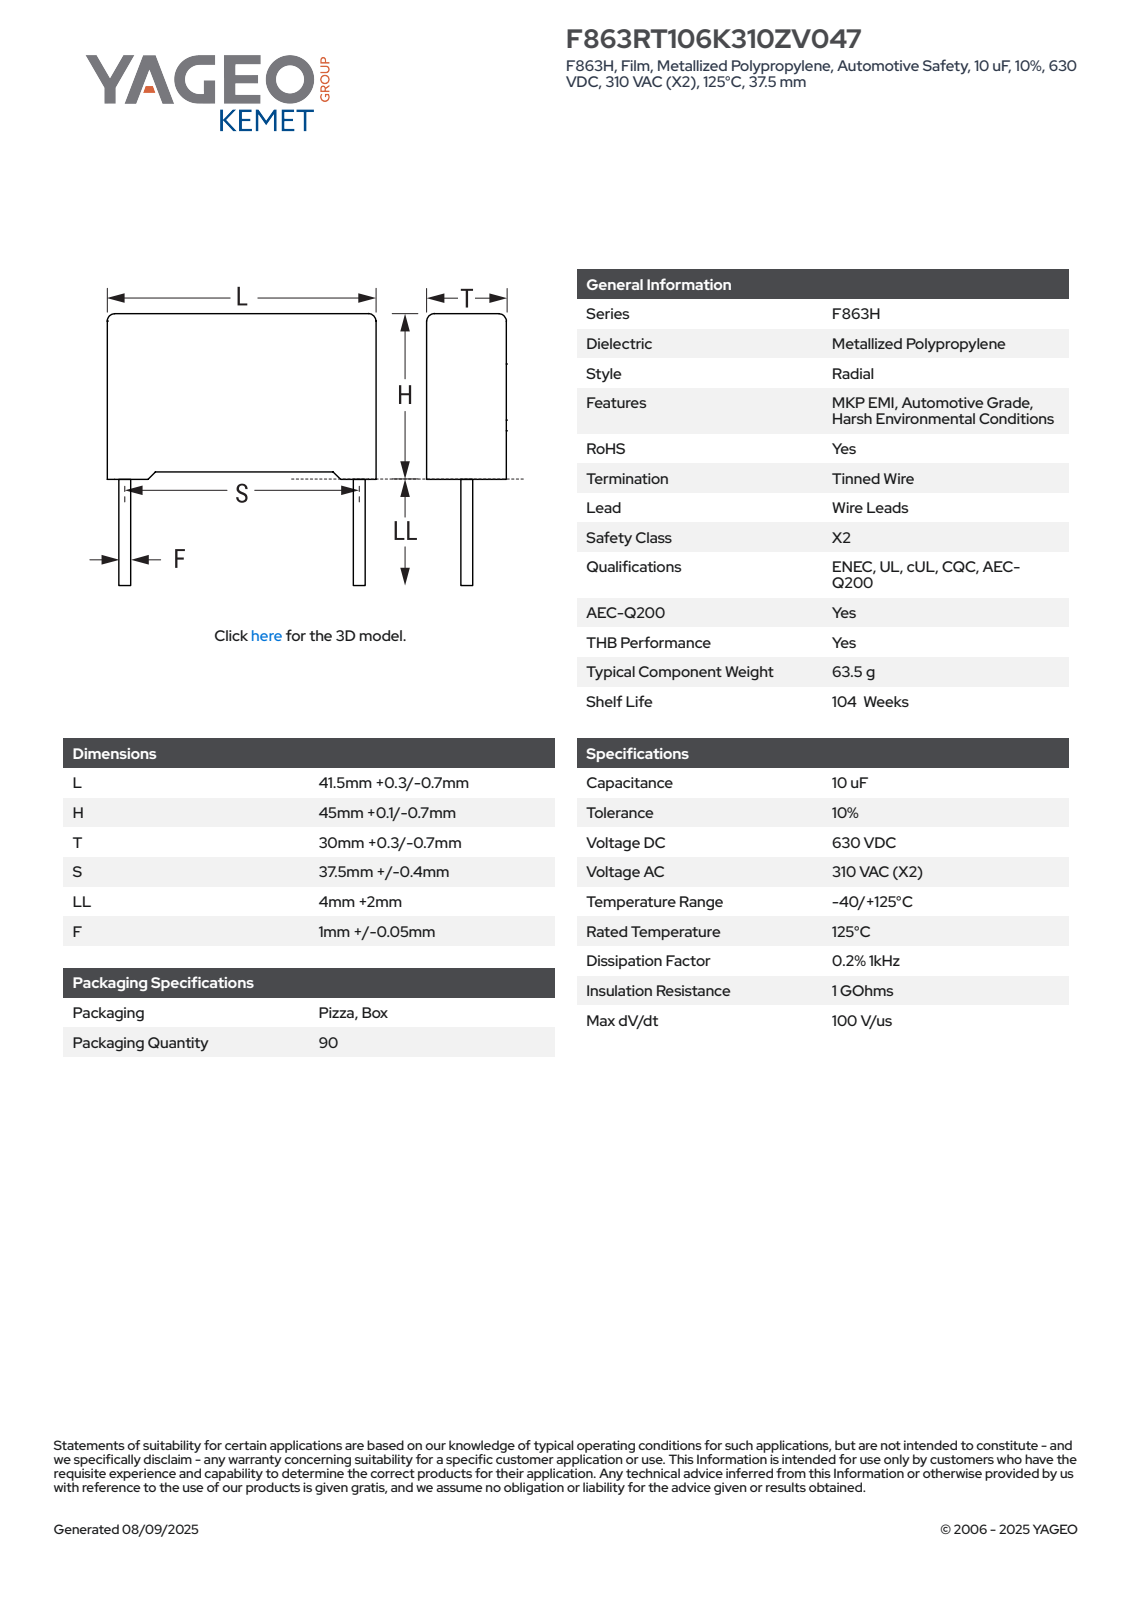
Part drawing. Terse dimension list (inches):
name: CFR_RB2_41.5X45X30_L41.8H45.1T30.3S37.5LL6F1.05
written by: SolidWorks 2021 (AUTOMOTIVE_DESIGN)
unit: in
bodies: 4 solids, 85 faces (77 planar, 8 cylindrical, 0 other)
size: 2.012 × 1.646 × 1.193
volume: 3.384 in³; area: 14.19 in²
bosses: 2× ⌀0.041
rounds: 4× R0.02
face distances: 1.193, 1.646, 1.714, 0.032, 1.746, 0.03, 0.061, 1.776, 0.055, 1.591
